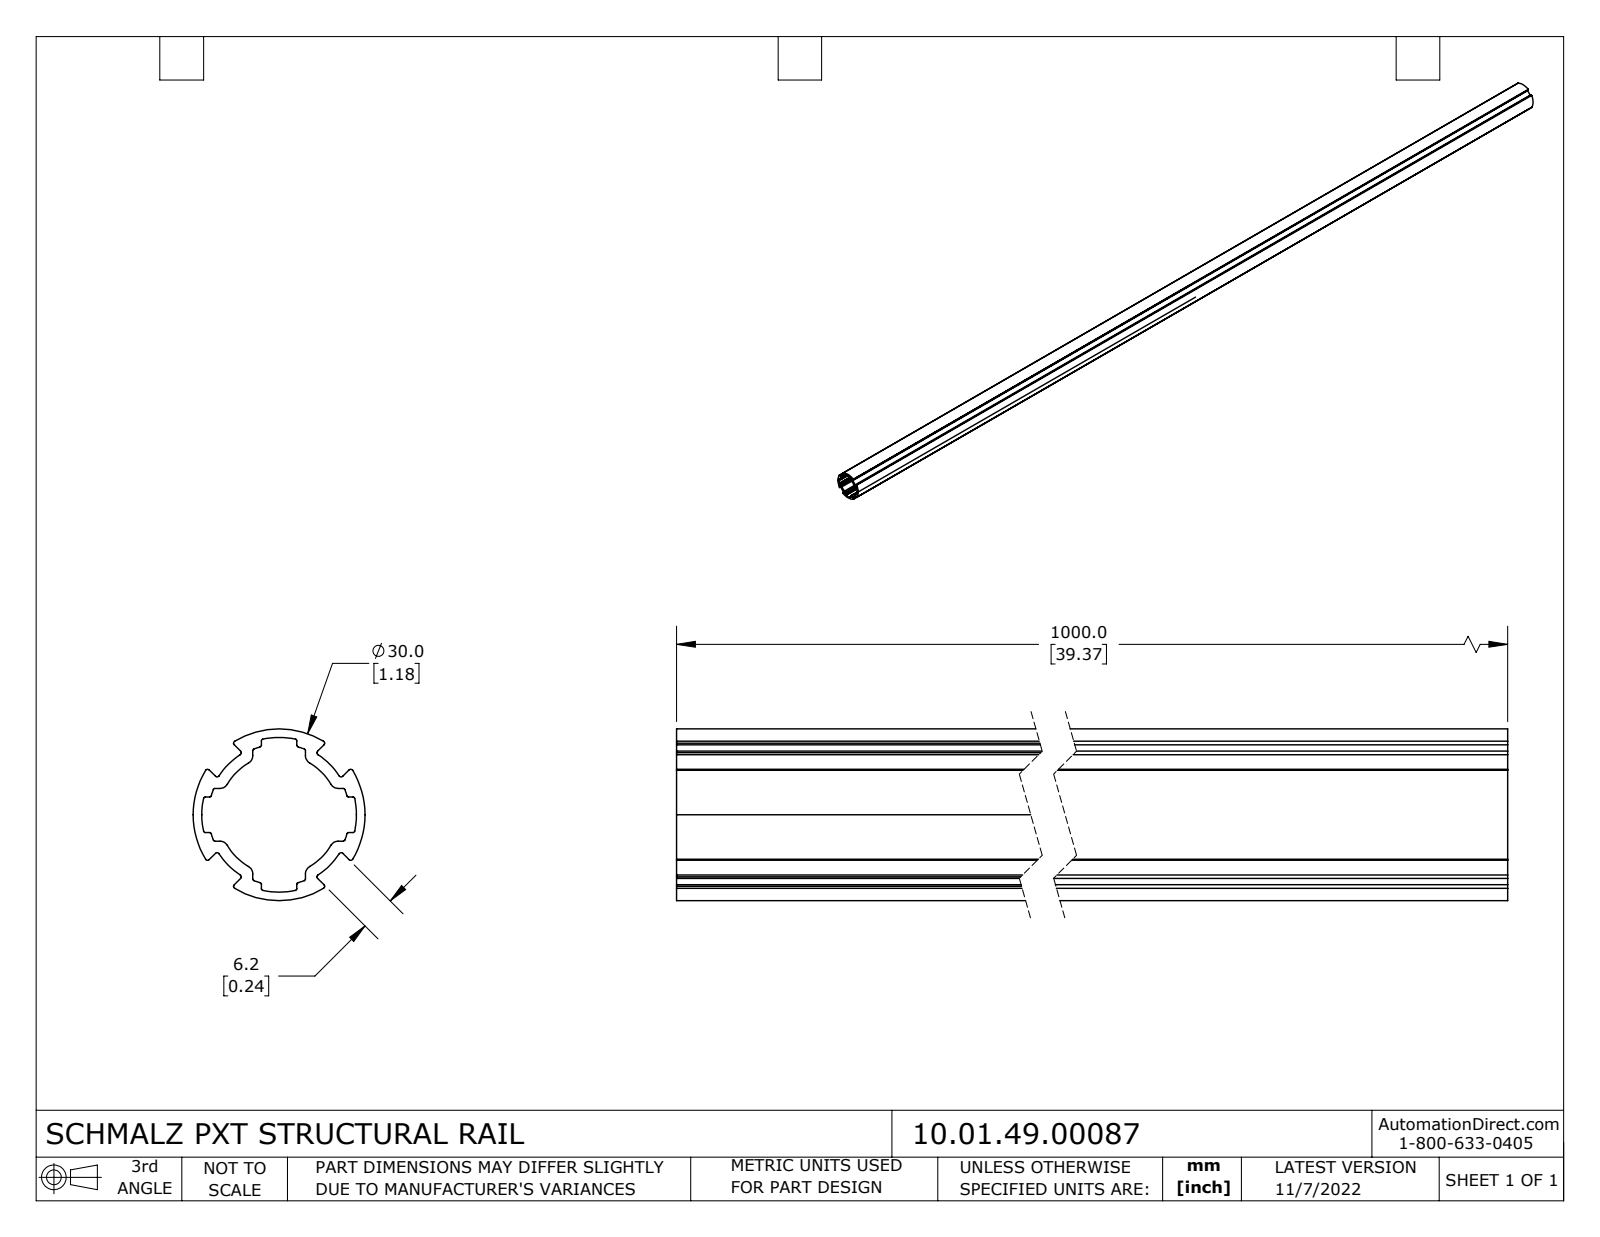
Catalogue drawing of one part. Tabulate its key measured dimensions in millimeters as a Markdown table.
| quantity | value |
| --- | --- |
| part name | 10.01.49.00087 |
| STEP written by | SolidWorks 2021 (CONFIG_CONTROL_DESIGN) |
| units | millimeters |
| bodies | 1 solid, 104 faces (26 planar, 78 cylindrical, 0 other) |
| overall size | 1000 × 30 × 30 |
| volume | 198 750 mm³ |
| surface area | 198 907 mm² |
| partial cylindrical surfaces (radius × count) | 0.3 × 24, 0.4 × 16, 1.5 × 8, 10.5 × 1, 12.3 × 1, 12.5 × 1, 13.5 × 1, 15 × 1 |
| main face-to-face distances | 6.2, 1.5, 7.7, 9.2, 1000 |
